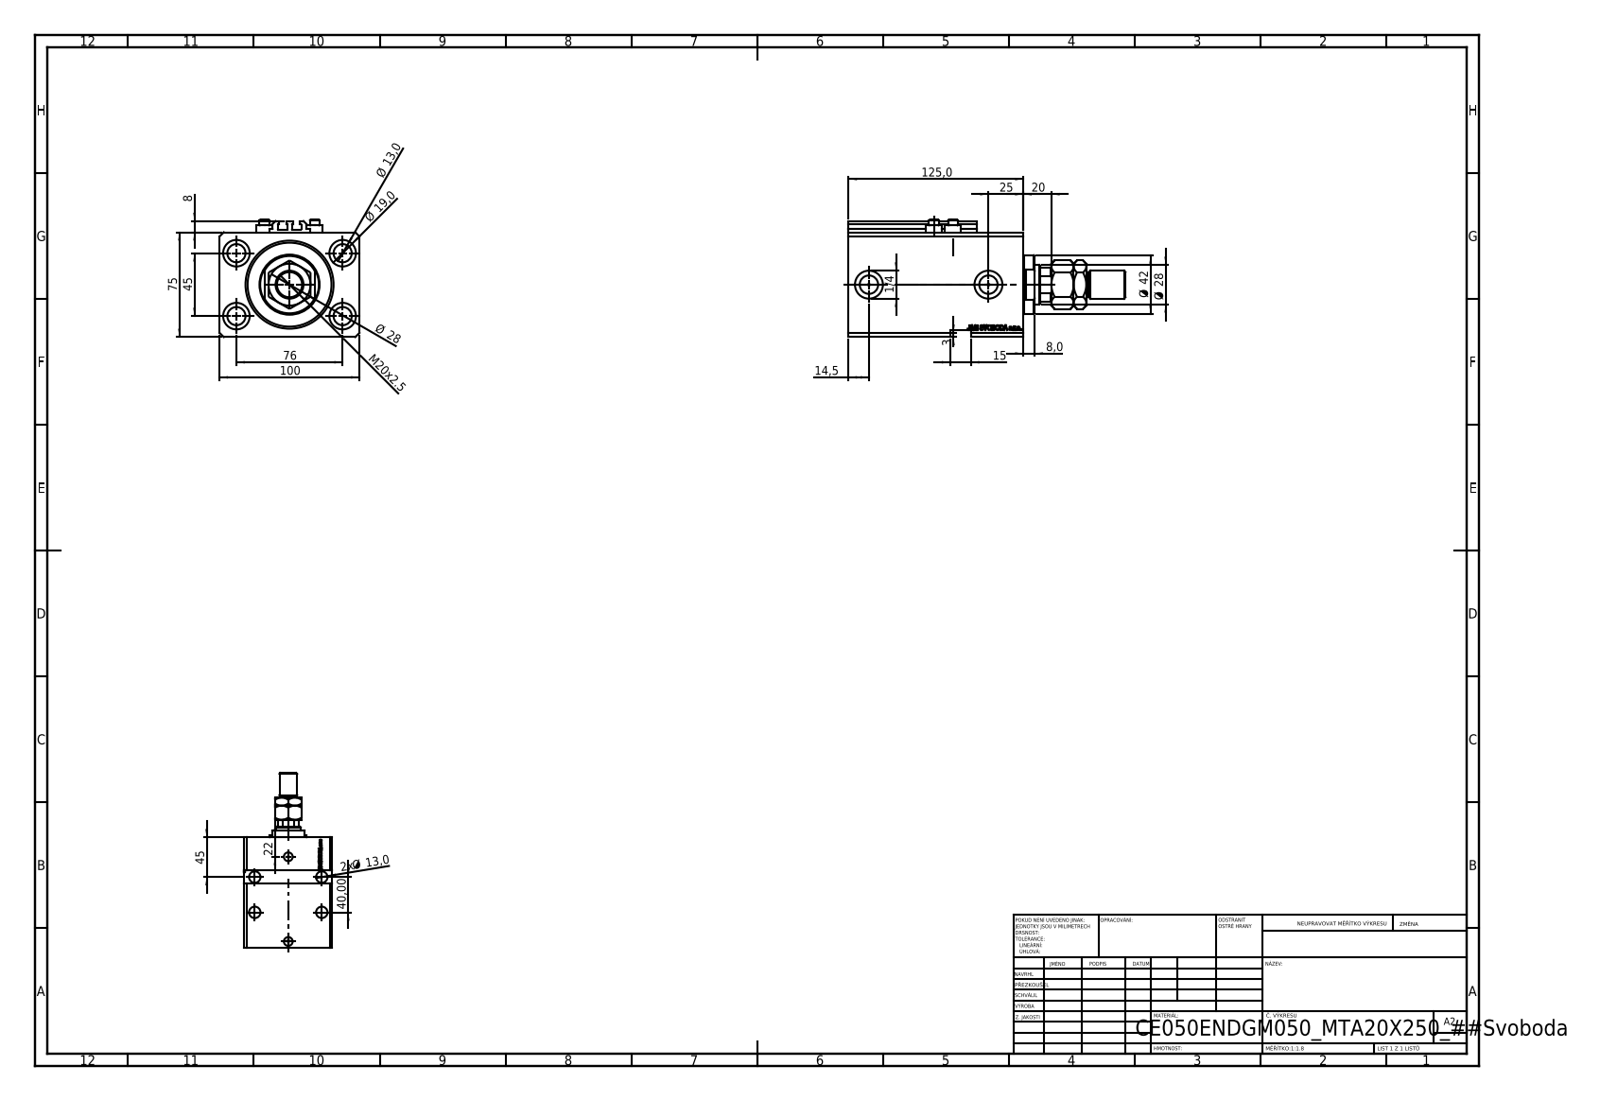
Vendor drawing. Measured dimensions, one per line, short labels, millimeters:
name: V250CE_C_VCP; V250CE_VC_E; MTA; V250CE_E_Body (+1 more)
written by: SolidWorks 2019 (CONFIG_CONTROL_DESIGN)
unit: mm
bodies: 9 solids, 1173 faces (554 planar, 162 cylindrical, 457 other)
size: 198 × 100 × 84
volume: 793 095 mm³; area: 157 383 mm²
holes: 8× ⌀13, 4× ⌀1.25, 4× ⌀4, 4× ⌀19, 2× ⌀10, 2× ⌀13.16, 2× ⌀20, 1× ⌀18.5, 1× ⌀28, 1× ⌀50, 1× ⌀63
bosses: 4× ⌀11.6, 4× ⌀7, 1× ⌀42, 1× ⌀20, 1× ⌀18
rounds: 10× R0.2, 1× R13.5
face distances: 75, 100, 20, 125, 11.9, 113.1, 105, 93.1, 70, 13
hole spacings: 44.16, 76, 13.6, 20.72, 27.59, 29, 33.62, 36
